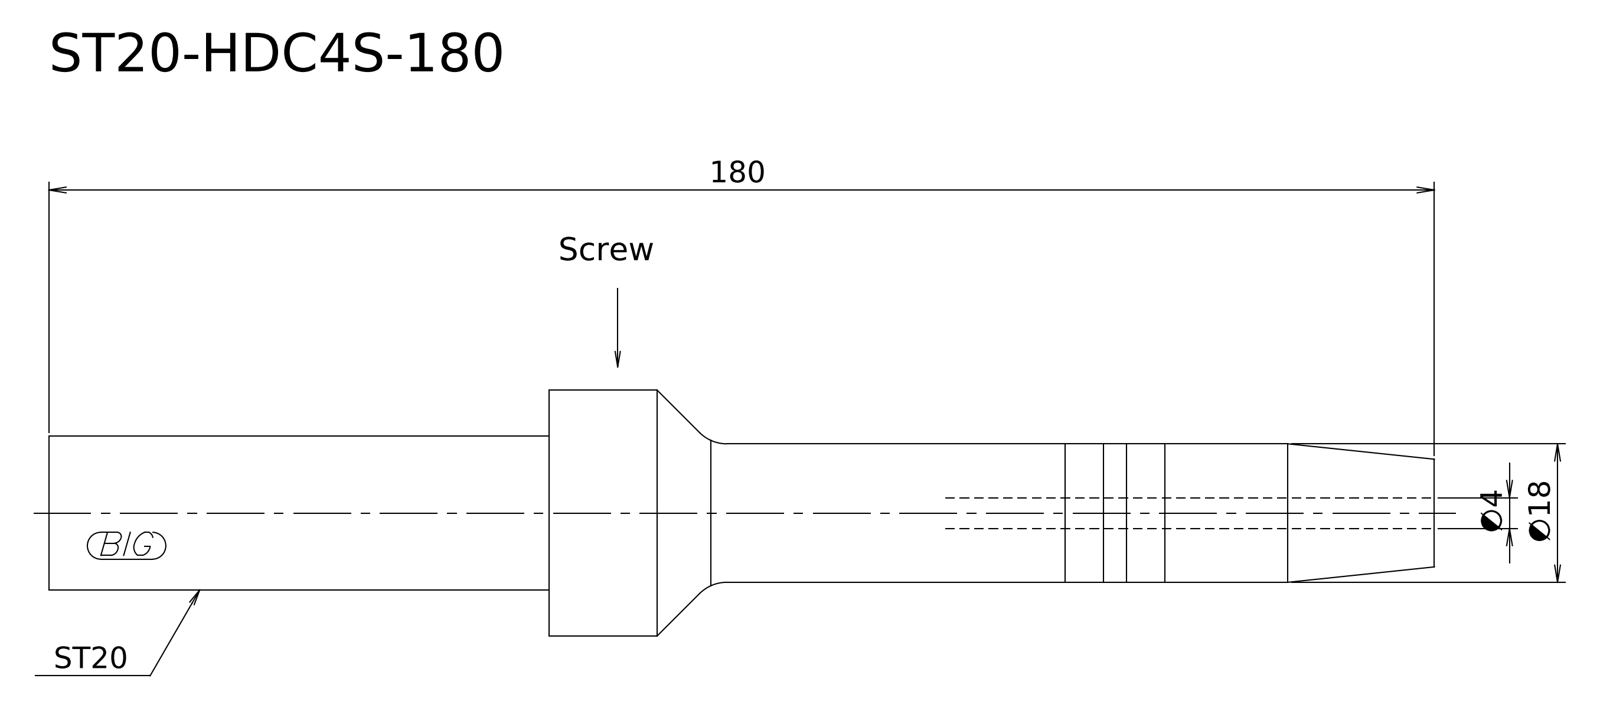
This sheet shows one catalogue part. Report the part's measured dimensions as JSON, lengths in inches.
{"step_written_by": "Kubotek KeyCreator V8.5.1 (14335) (CONFIG_CONTROL_DESIGN)", "units": "inches", "bodies": {"solids": 1, "faces": 9, "planar": 3, "cylindrical": 3, "other": 3}, "overall_size": [7.087, 1.26, 1.26], "volume_in3": 3.811, "surface_area_in2": 19.9, "round_bosses_or_shafts": [[1.26, 1], [0.787, 1]], "face_to_face_distances": [2.559, 4.528, 7.087]}
